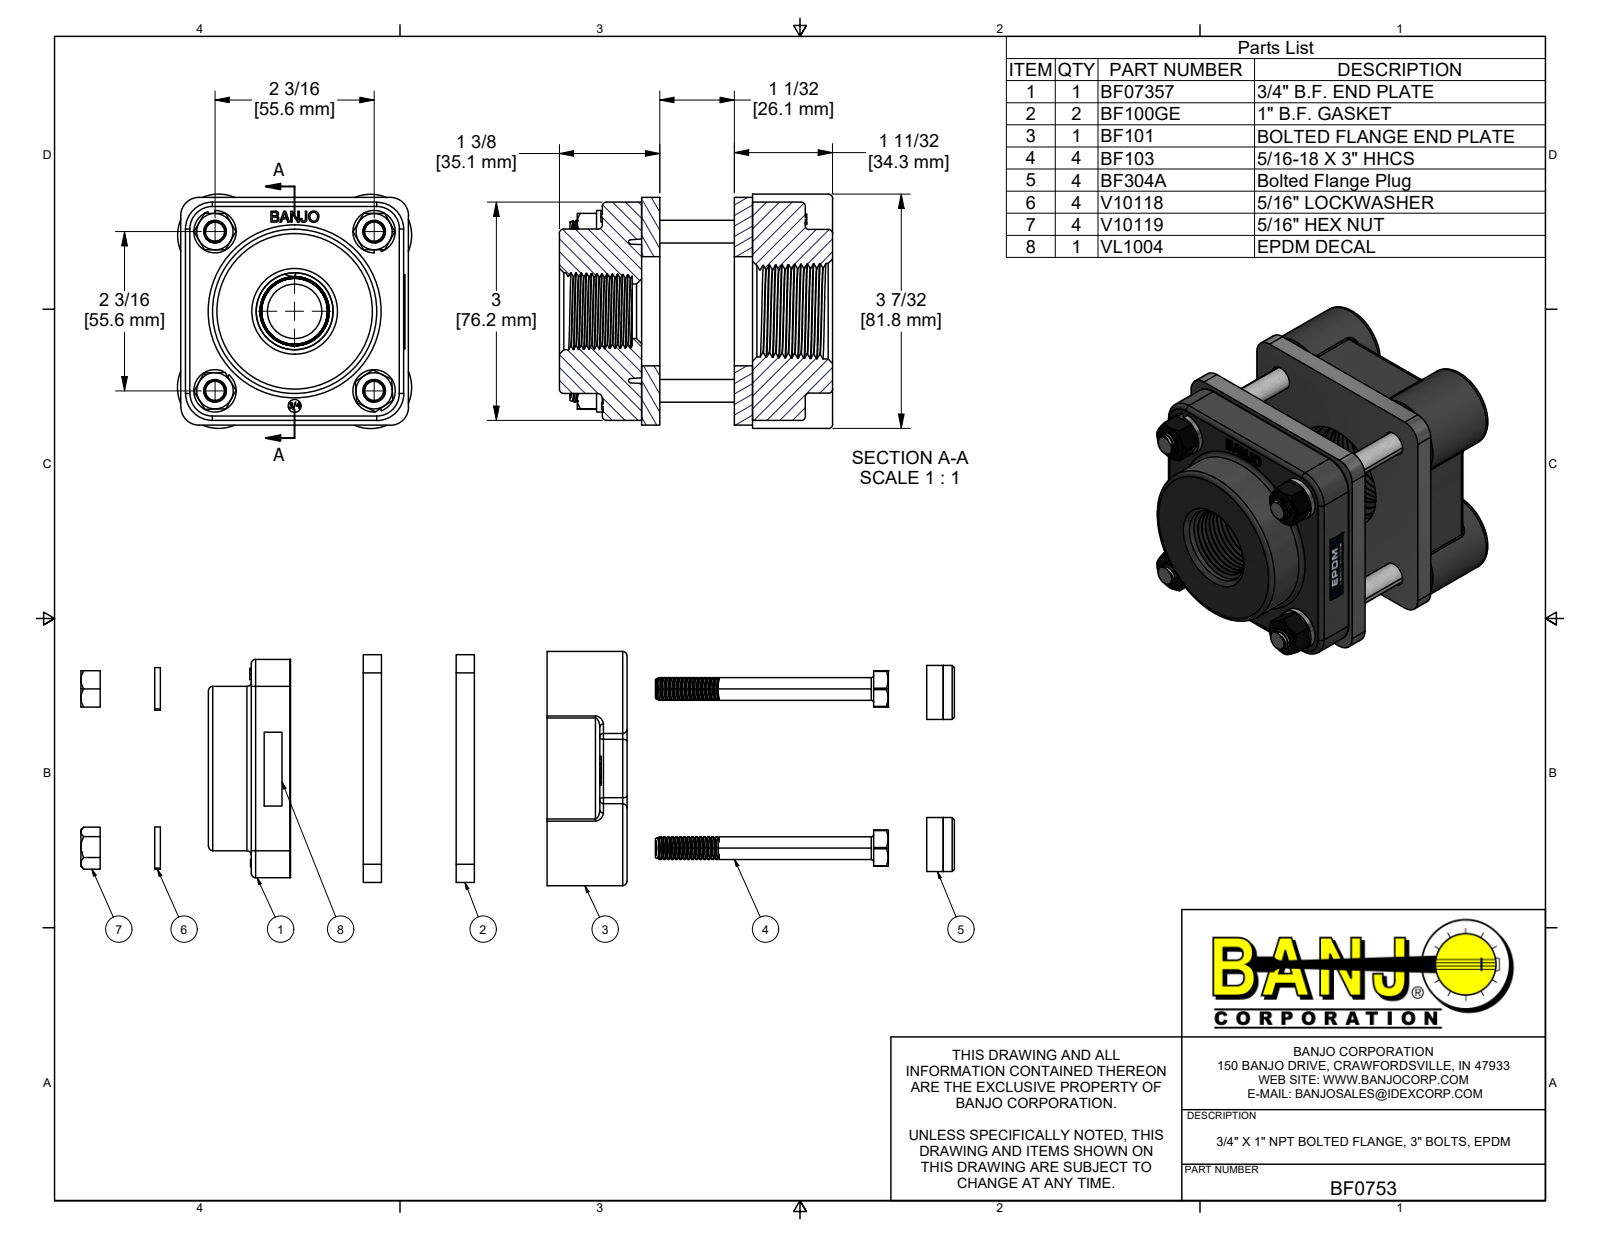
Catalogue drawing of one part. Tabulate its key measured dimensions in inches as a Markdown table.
| quantity | value |
| --- | --- |
| part name | BF0753; V10119; BF101; BF07357 (+6 more) |
| STEP written by | Autodesk Inventor 2019 (AUTOMOTIVE_DESIGN) |
| units | inches |
| bodies | 21 solids, 1637 faces (518 planar, 452 cylindrical, 667 other) |
| overall size | 17.114 × 3.22 × 3.22 |
| volume | 19.02 in³ |
| surface area | 308.1 in² |
| round holes (diameter × count) | 0.252 × 4, 0.322 × 4, 0.34 × 4, 0.344 × 4, 0.35 × 4, 0.72 × 4, 0.745 × 4, 0.18 × 1, 0.75 × 1, 1.5 × 1 |
| round bosses / shafts (diameter × count) | 0.268 × 60, 0.742 × 4, 0.583 × 4, 0.313 × 4, 2.26 × 1 |
| partial cylindrical surfaces (radius × count) | 0.06 × 20, 0.05 × 8, 0.134 × 8, 0.25 × 4, 0.284 × 4, 0.37 × 4, 0.565 × 4, 0.315 × 1 |
| main face-to-face distances | 0.25, 1.276, 1.526, 1.026, 0.065, 3.065, 2.376, 1.1, 2.626, 1.35 |
| hole center spacings | 2.139, 2.142, 2.146, 2.19, 2.194, 2.196, 0.07, 0.072 |
